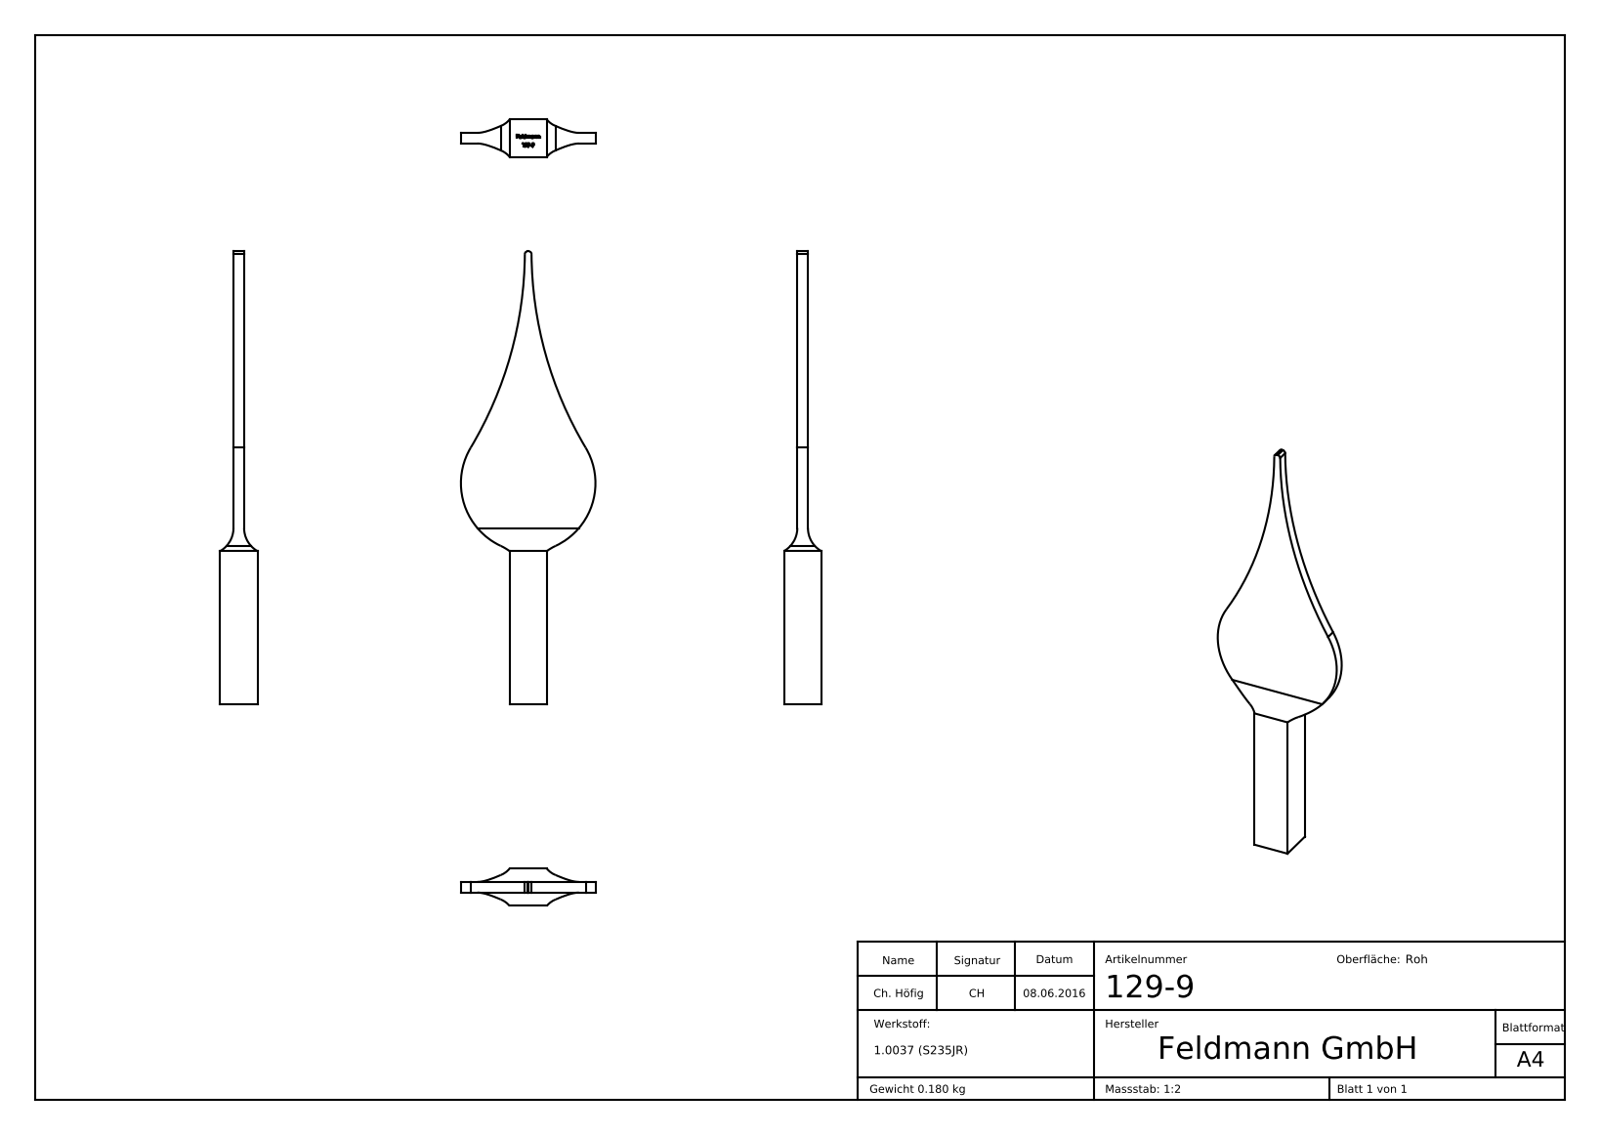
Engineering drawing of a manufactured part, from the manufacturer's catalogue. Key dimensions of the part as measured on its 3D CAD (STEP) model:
Part name (STEP PRODUCT): 129-9
STEP written by: SolidWorks 2015 (CONFIG_CONTROL_DESIGN)
Units: millimetres
Bodies: 1 solid, 185 faces (102 planar, 11 cylindrical, 72 other)
Overall size (bounding box): 170 × 50.5 × 14
Volume: 23 060 mm³ · Surface area: 10 229 mm²
Partial cylindrical surfaces — rounded edges, fillets, slot ends (radius × count): R1 ×2, R10 ×2, R20 ×2, R26 ×2, R143.73 ×2
Main face-to-face distances: 4, 5, 9, 14, 170, 169.9, 0.39, 2.97, 1.26, 7
